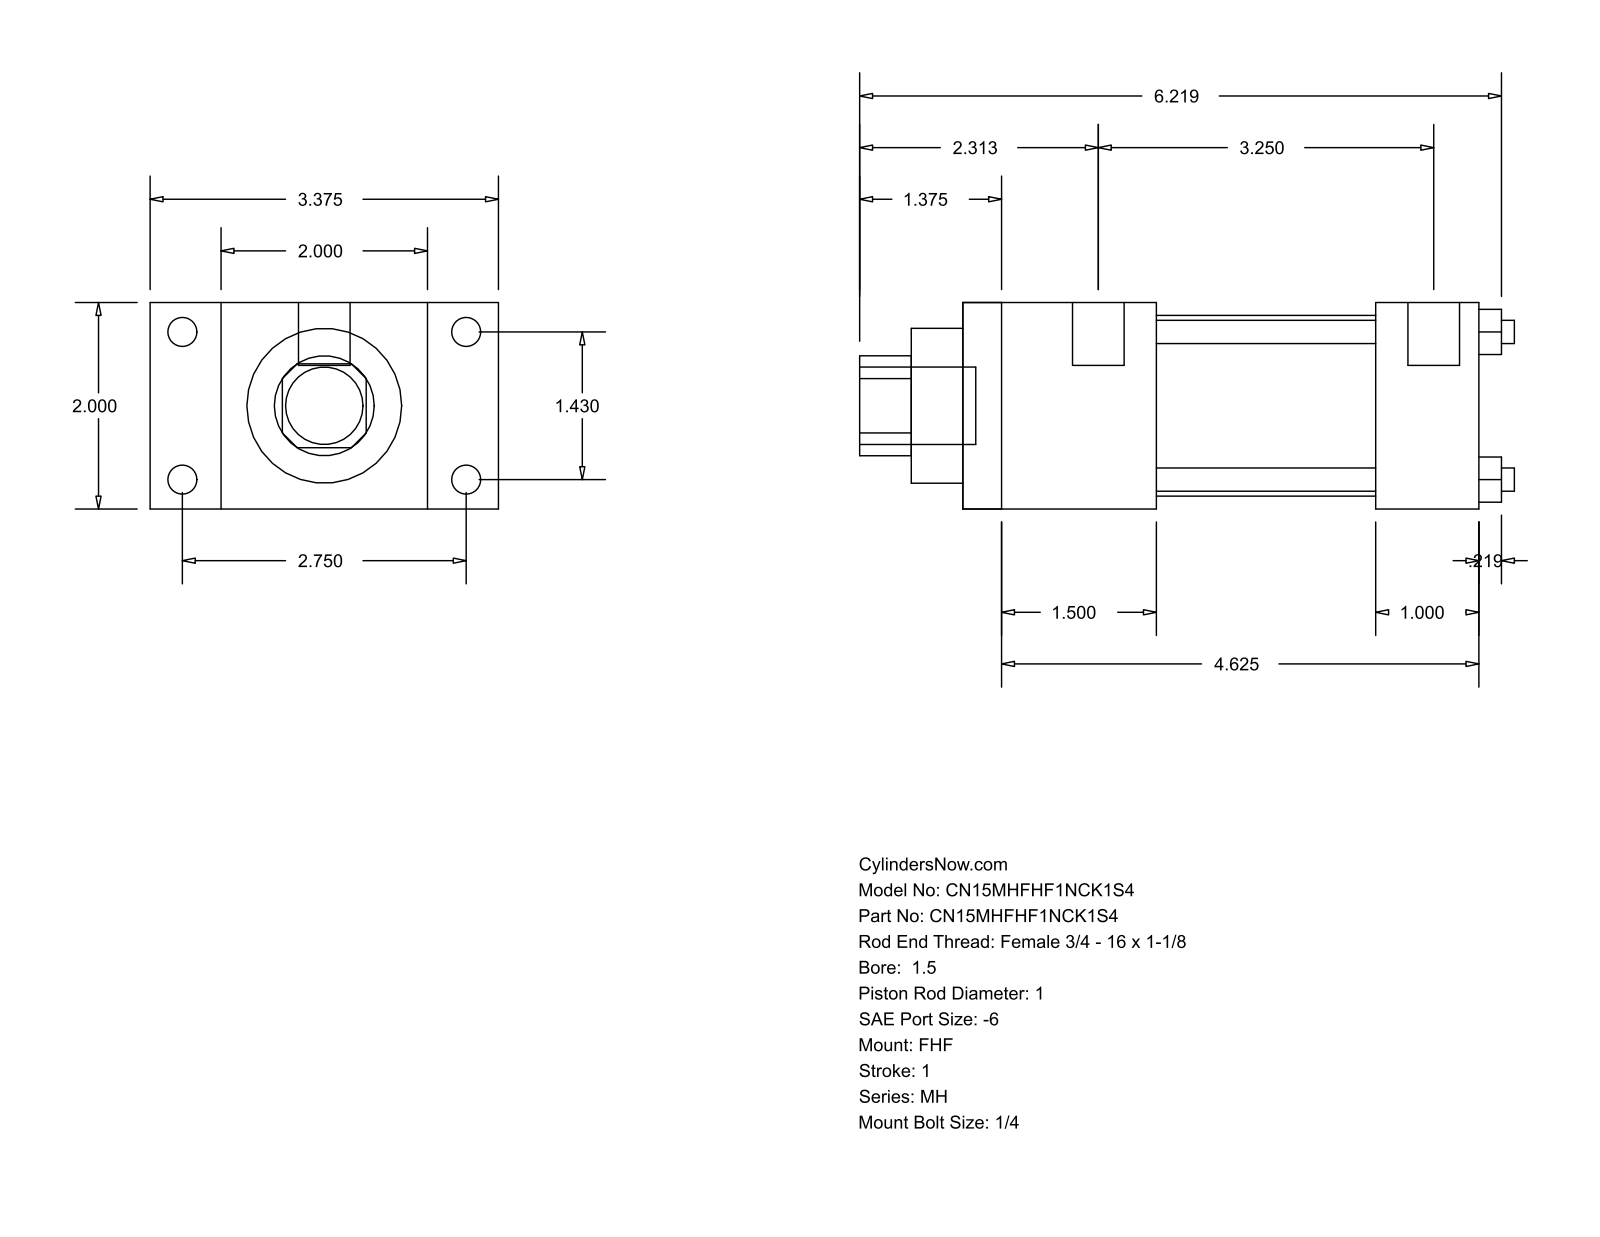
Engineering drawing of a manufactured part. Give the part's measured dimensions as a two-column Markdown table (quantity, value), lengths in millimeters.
| quantity | value |
| --- | --- |
| part name | MH_FHF__0150_1 |
| STEP written by | GSSL Pune (CONFIG_CONTROL_DESIGN) |
| units | millimeters |
| bodies | 0 solids, 88 faces (60 planar, 28 cylindrical, 0 other) |
| overall size | 161.13 × 85.72 × 50.8 |
| round holes (diameter × count) | 5.71 × 4, 25.4 × 1, 38.1 × 1, 44.45 × 1 |
| round bosses / shafts (diameter × count) | 7.14 × 4, 5.56 × 4, 12.7 × 2, 19.05 × 1 |
| partial cylindrical surfaces (radius × count) | 12.29 × 1 |
| main face-to-face distances | 50.8, 17.46, 68.26, 47.63, 85.72, 127, 79.37, 25.4, 101.6, 53.97 |
| hole center spacings | 25.68, 36.32, 51.36 |
